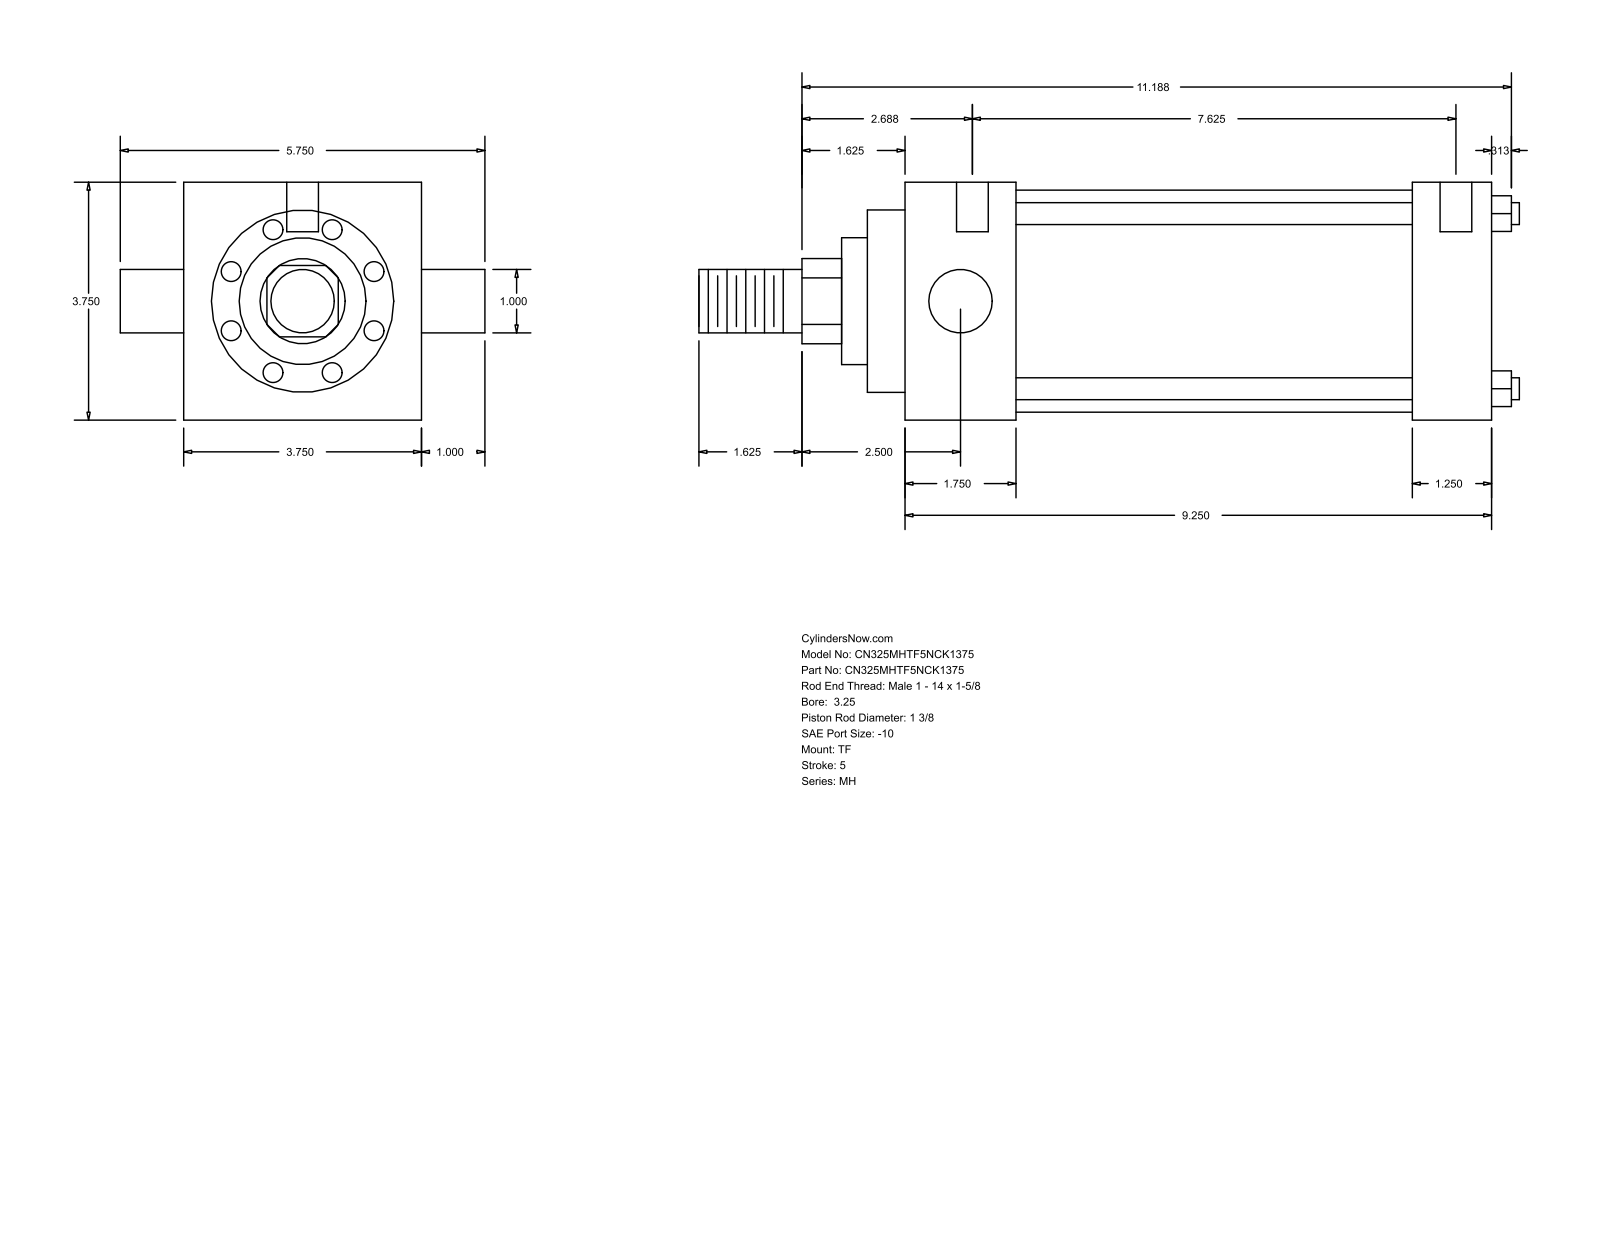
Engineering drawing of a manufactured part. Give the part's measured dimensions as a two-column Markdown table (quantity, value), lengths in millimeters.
| quantity | value |
| --- | --- |
| part name | MH_TF__0325_1.375 |
| STEP written by | GSSL Pune (CONFIG_CONTROL_DESIGN) |
| units | millimeters |
| bodies | 0 solids, 86 faces (61 planar, 25 cylindrical, 0 other) |
| overall size | 328.61 × 146.05 × 95.25 |
| round holes (diameter × count) | 5.56 × 3, 12.7 × 2 |
| round bosses / shafts (diameter × count) | 8.76 × 4, 25.4 × 2, 88.9 × 1, 73.03 × 1, 50.8 × 1, 34.92 × 1 |
| partial cylindrical surfaces (radius × count) | 17.06 × 1 |
| main face-to-face distances | 95.24, 234.96, 44.45, 203.2, 158.75, 190.51, 31.76, 15.08, 59.53, 218.28 |
| hole center spacings | 1.59, 4.76, 193.68, 195.27, 198.44, 200.03 |
